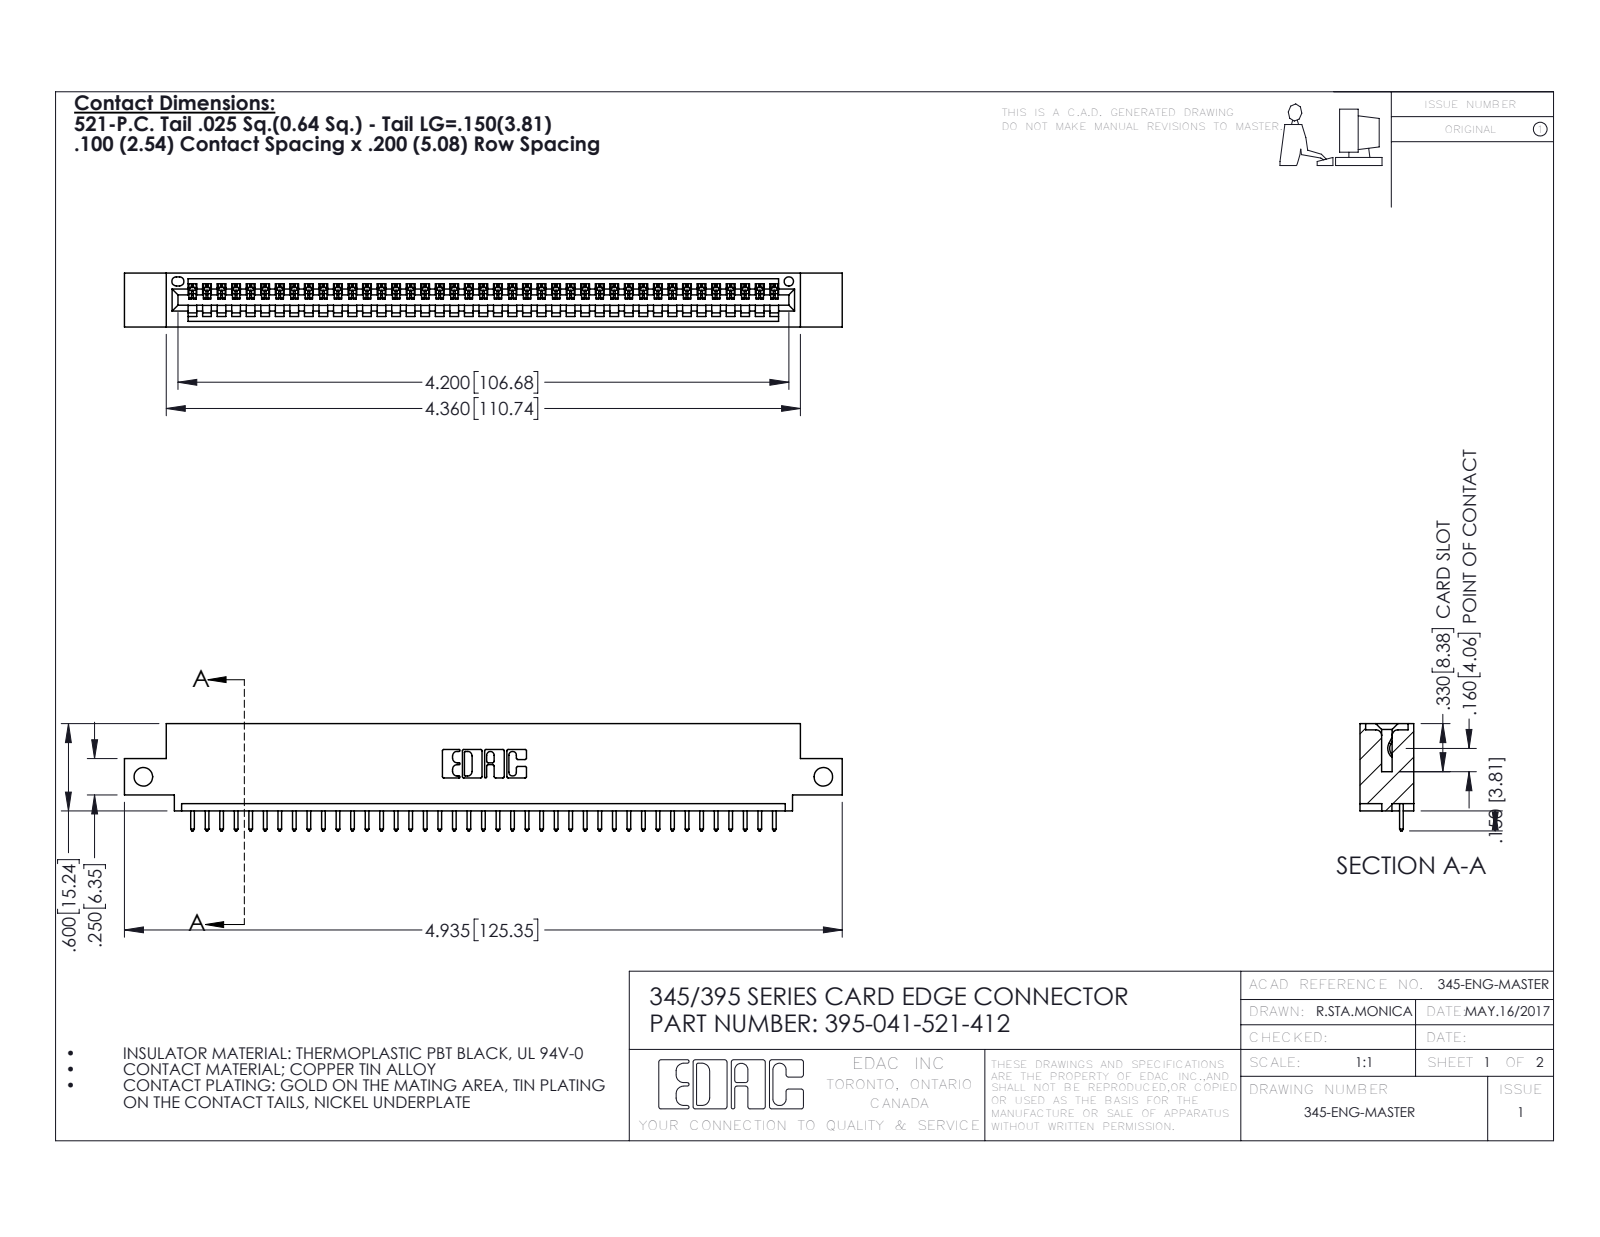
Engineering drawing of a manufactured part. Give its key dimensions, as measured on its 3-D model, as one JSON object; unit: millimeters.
{"part_name": "345-292-001_345-293-121; 345 Part_0.110 Offset - Side Mount; 395-041-521-412", "step_written_by": "SolidWorks 2016 (CONFIG_CONTROL_DESIGN)", "units": "millimeters", "bodies": {"solids": 42, "faces": 2508, "planar": 1724, "cylindrical": 784, "other": 0}, "overall_size": [125.3, 18.7, 9.4], "volume_mm3": 11600, "surface_area_mm2": 14910, "round_holes": [[3.3, 2], [1.6, 1]], "partial_cylinders_radius": [[0.2, 82], [0.3, 82], [0.3, 22], [0.2, 6], [0.8, 6], [0.7, 3], [0.8, 2], [1, 2]], "face_to_face_distances": [7.6, 1.8, 9.4, 5.1, 2.5, 6.9, 0.6, 5.7, 3.8, 1.8], "hole_center_spacings": [118.7]}
